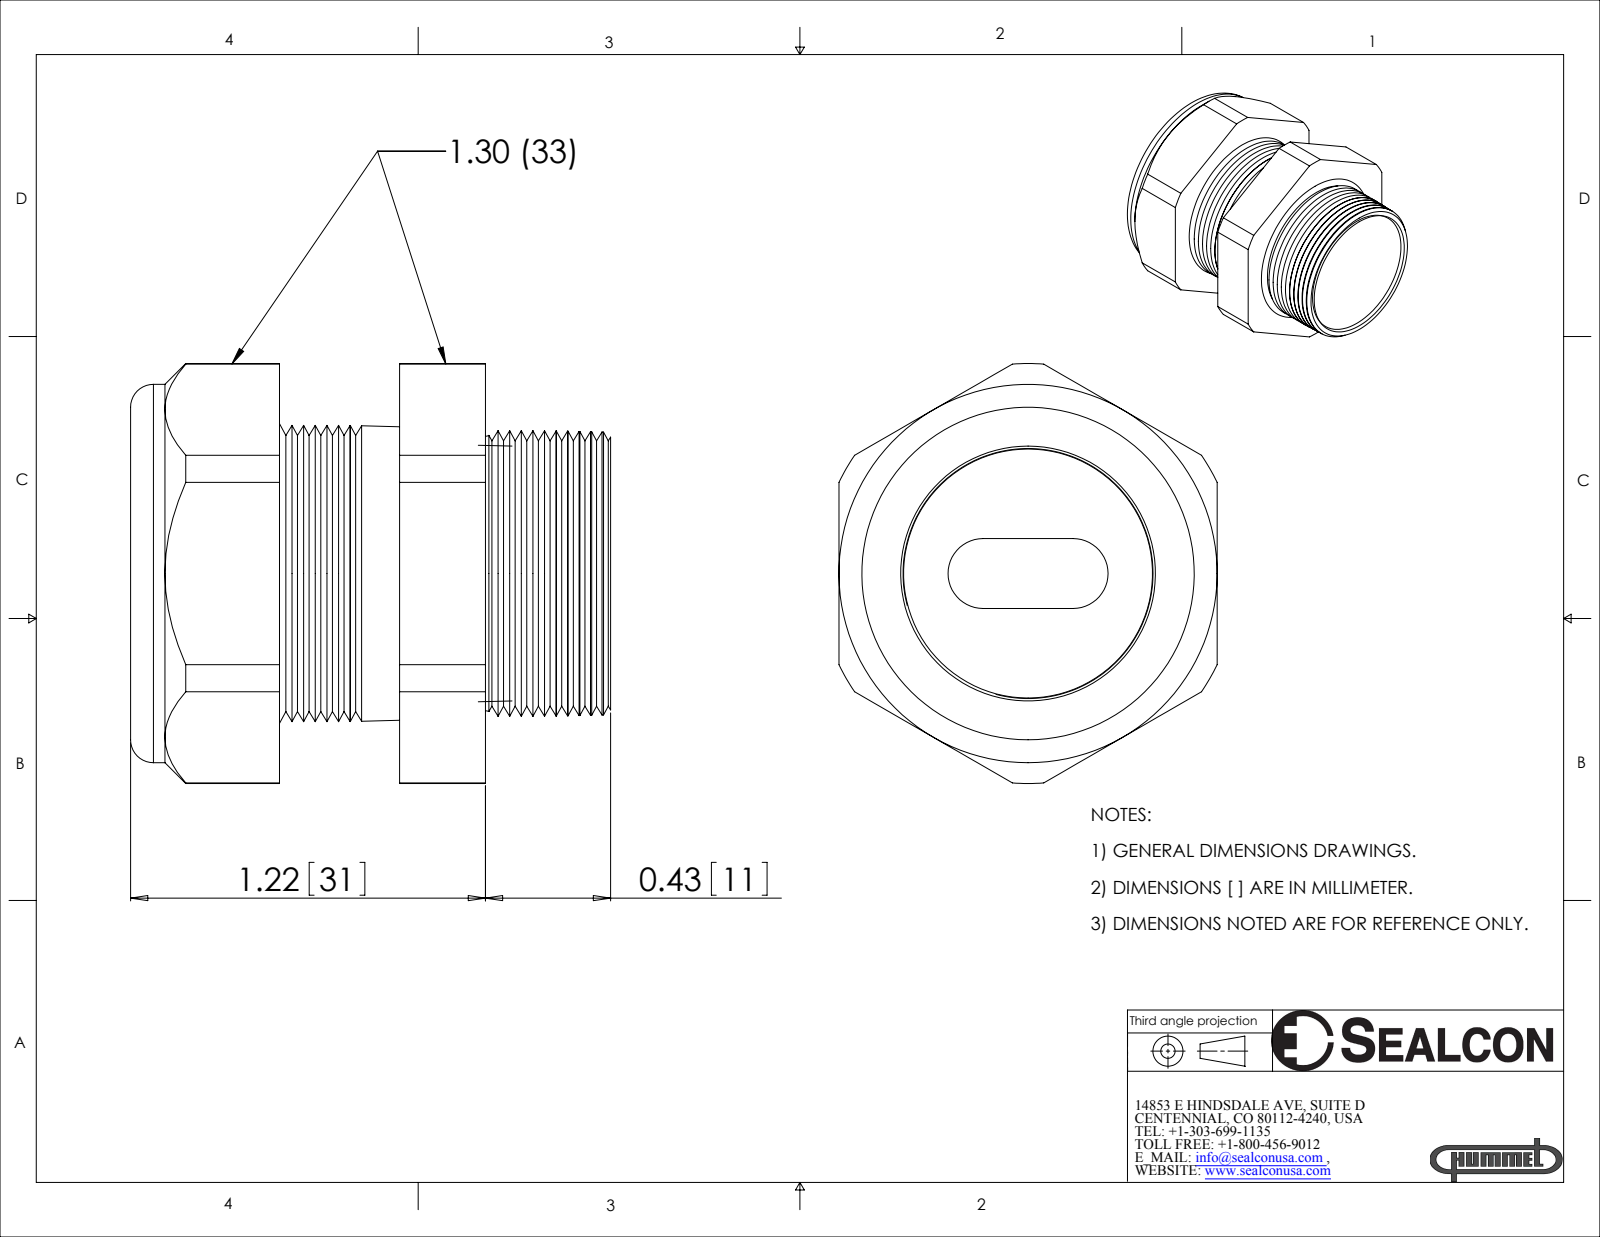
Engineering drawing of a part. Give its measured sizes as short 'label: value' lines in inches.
name: CD25MS-01
written by: SolidWorks 2008 (CONFIG_CONTROL_DESIGN)
unit: in
bodies: 2 solids, 139 faces (21 planar, 20 cylindrical, 98 other)
size: 1.65 × 1.443 × 1.3
volume: 0.955 in³; area: 18.04 in²
holes: 1× ⌀0.876
bosses: 1× ⌀1.3, 1× ⌀0.856
rounds: 2× R0.12, 1× R0.721
face distances: 1.3, 0.925, 0.512, 0.413, 1.22, 0.708, 0.295, 0.394, 0.118, 0.531
